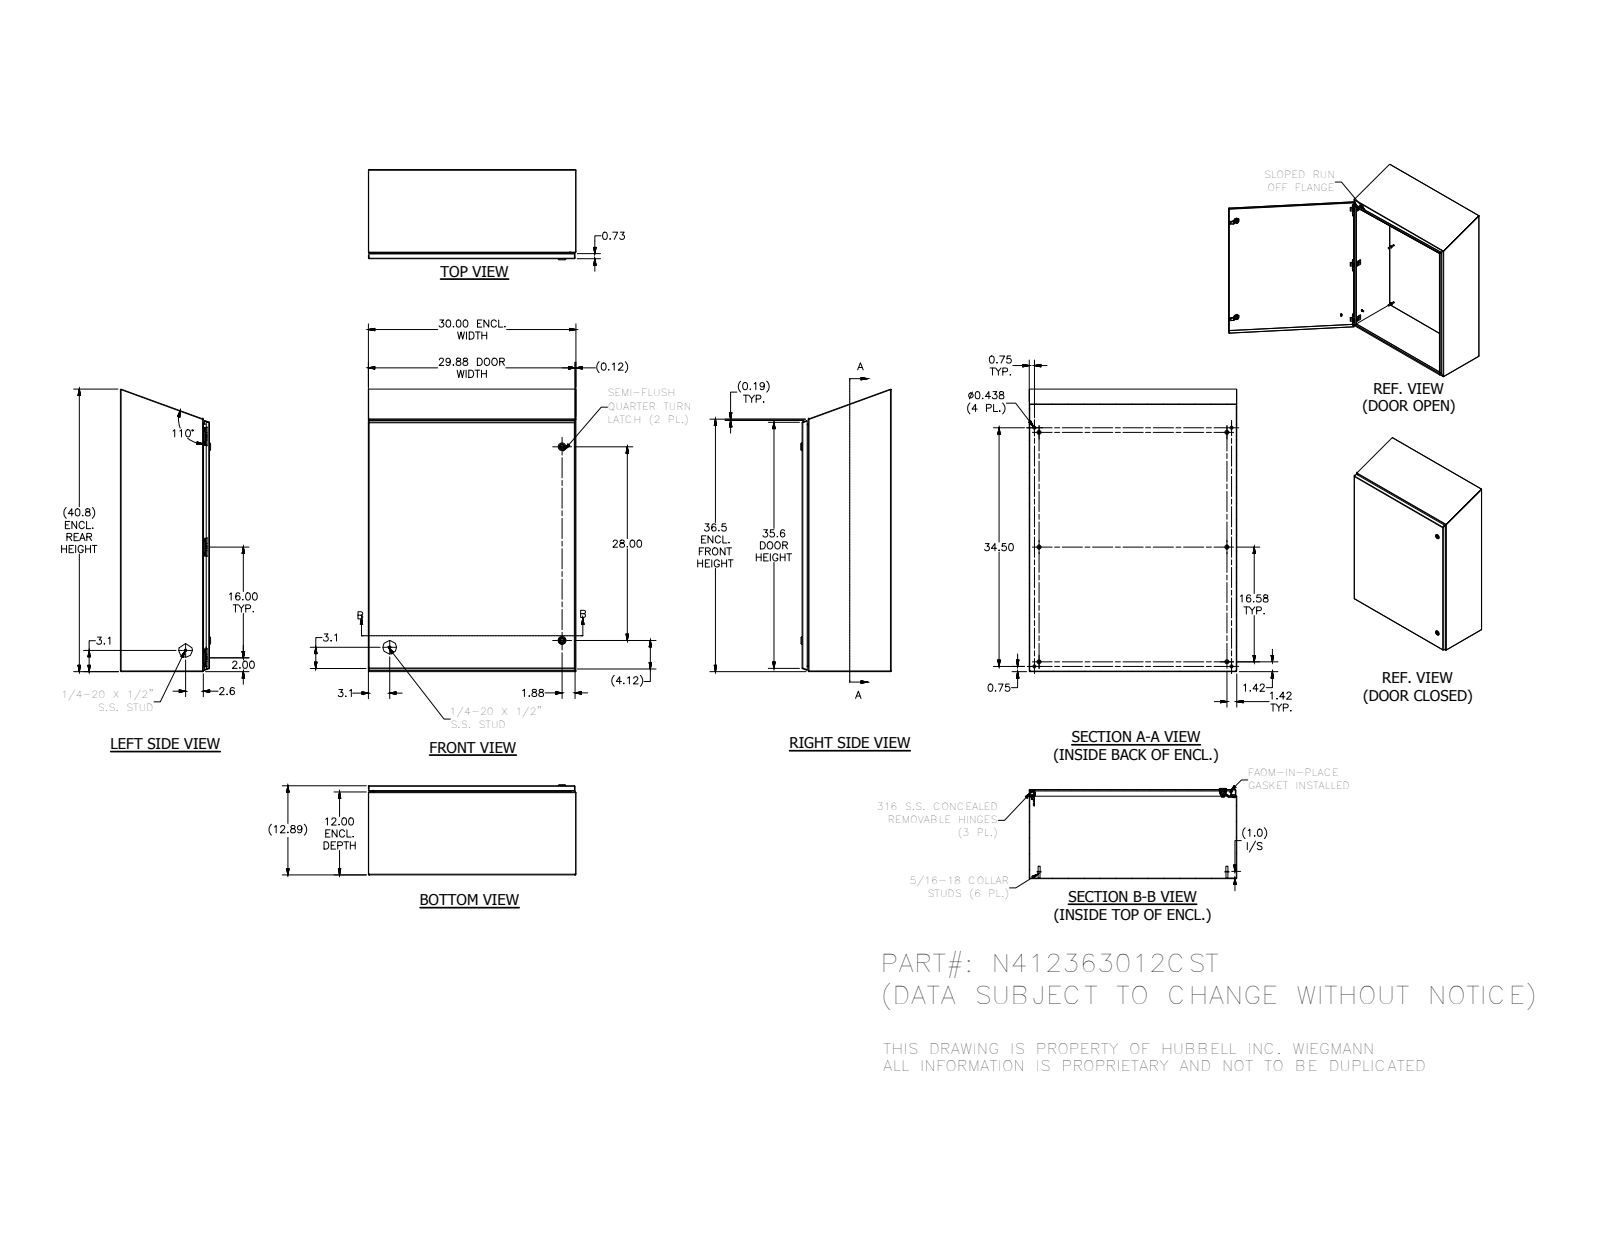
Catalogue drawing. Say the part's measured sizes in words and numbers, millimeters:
The part is named "N412_CST-assm; N412363012CSTB3S; HFW3161; HFW328176 (+8 more)". Its 3-D file was written by "Autodesk Inventor 2012 (AUTOMOTIVE_DESIGN)". It is 51 solids with 2370 faces: 900 planar, 872 cylindrical and 598 other. Overall it measures 1037.5 by 762 by 331.3 millimeters. Its volume is 5 155 000 cubic millimeters and its surface area 5 527 000 square millimeters. Round holes: 6 of diameter 2.4, 6 of diameter 3.9, 6 of diameter 4.2, 6 of diameter 4.4, 6 of diameter 4.7, 4 of diameter 4, 4 of diameter 11.1, 2 of diameter 5, 2 of diameter 8, 2 of diameter 10, 2 of diameter 10.2, 2 of diameter 16.1. Round bosses or shafts: 14 of diameter 6.4, 6 of diameter 14.3, 6 of diameter 9.1, 6 of diameter 8.1, 6 of diameter 7.6, 6 of diameter 7, 6 of diameter 6.5, 6 of diameter 4.2. Partial cylindrical surfaces (rounded edges, fillets, slot ends): 54 of radius 0.3, 38 of radius 1.3, 33 of radius 0.8, 26 of radius 0.4, 24 of radius 3.2, 23 of radius 0.5, 19 of radius 2.7, 12 of radius 0.8. The main face-to-face distances are 1.9, 325.5, 323.6, 327.3, 760.1, 758.2, 762, 302.9, 22.5, 20.7. The hole center spacings are 406.4, 812.8, 406.6, 12.7, 16.7, 16.8, 33.2, 33.3.
